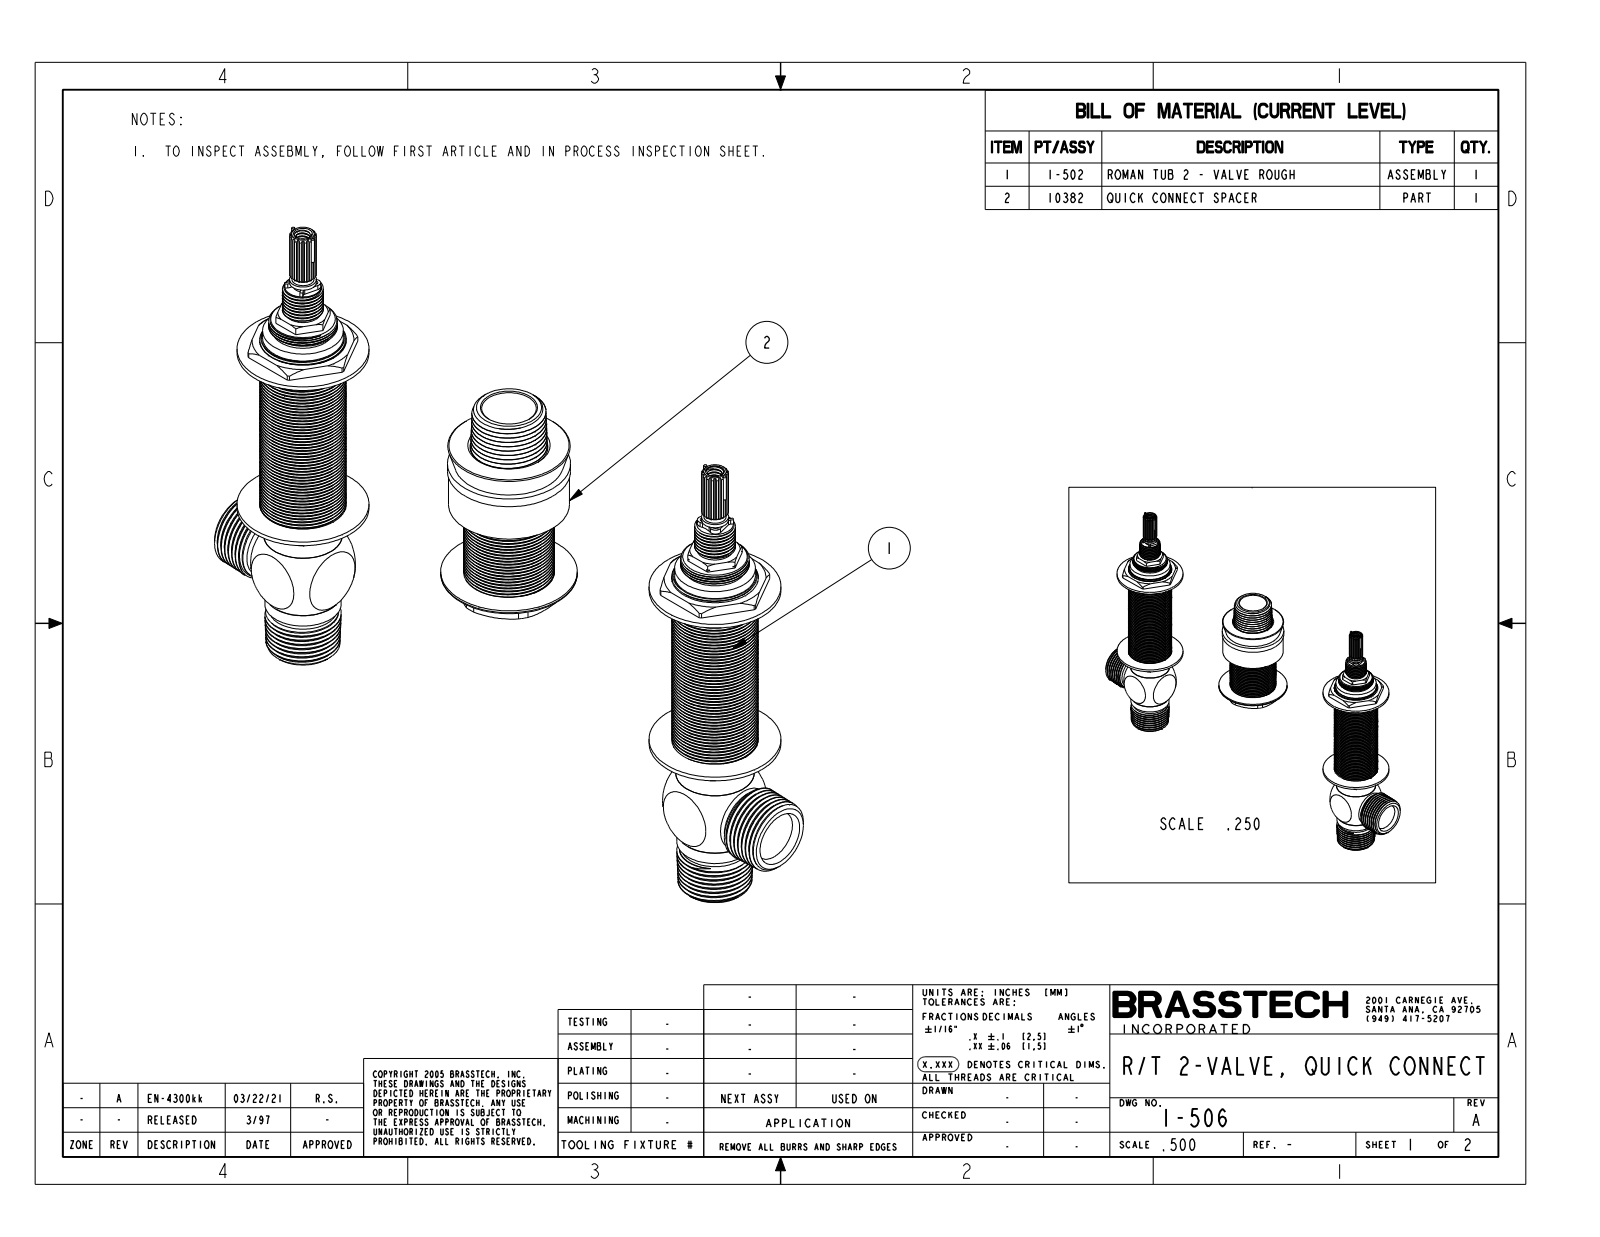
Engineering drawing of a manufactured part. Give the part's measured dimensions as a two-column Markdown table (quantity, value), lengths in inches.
| quantity | value |
| --- | --- |
| part name | 1-506 |
| STEP written by | CREO PARAMETRIC BY PTC INC, 2018400 (AUTOMOTIVE_DESIGN) |
| units | inches |
| bodies | 3 solids, 1207 faces (232 planar, 522 cylindrical, 453 other) |
| overall size | 10.52 × 6.941 × 1.875 |
| volume | 17.03 in³ |
| surface area | 122.7 in² |
| round holes (diameter × count) | 0.196 × 2, 0.201 × 2, 0.709 × 1, 1.406 × 1 |
| round bosses / shafts (diameter × count) | 1.811 × 2, 1.187 × 2, 1.11 × 2, 1.075 × 2, 1.047 × 2, 0.945 × 2, 0.929 × 2, 0.835 × 2 |
| partial cylindrical surfaces (radius × count) | 0.04 × 8, 0.08 × 8, 0.164 × 2, 0.26 × 2, 0.3 × 2, 0.775 × 2, 0.758 × 1 |
| main face-to-face distances | 0.061, 0.04, 2.613, 2.573, 1.688, 1.749, 0.864, 2.552, 0.824, 2.512 |
| hole center spacings | 4, 8 |
